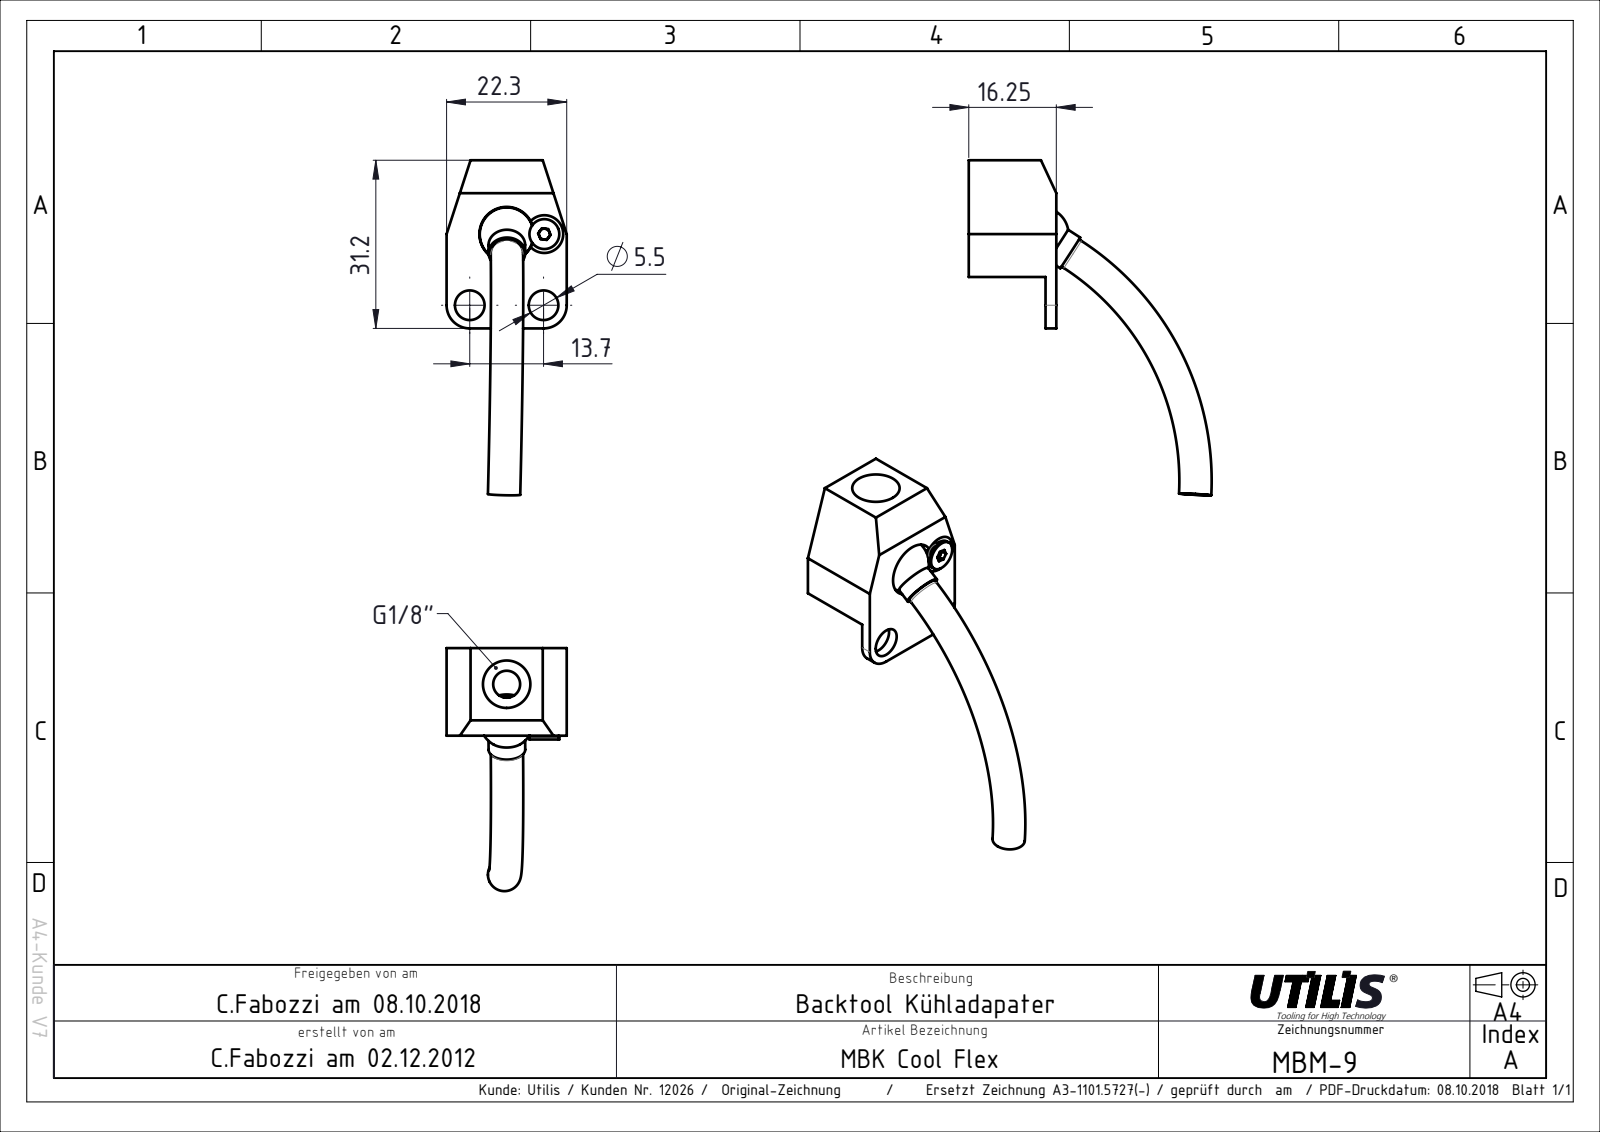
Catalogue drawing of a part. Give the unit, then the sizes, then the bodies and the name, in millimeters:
Units: millimetres
Overall size (bounding box): 62.16 × 45.09 × 22.3
Round holes (diameter × count): ⌀5.5 ×2, ⌀5 ×1
Round bosses / shafts (diameter × count): ⌀6.8 ×1, ⌀6 ×1, ⌀5.54 ×1, ⌀3 ×1
Partial cylindrical surfaces — rounded edges, fillets, slot ends (radius × count): R4.3 ×2, R26.5 ×1
Main face-to-face distances: 16.25, 14.25, 2, 22.3, 31.2, 16.96, 2.71, 0.71, 10, 8.96
Hole centre spacings: 13.7
Volume: 7 420 mm³ · Surface area: 4 964 mm²
Bodies: 3 solids, 58 faces (27 planar, 17 cylindrical, 14 other)
Part name (STEP PRODUCT): MSP-88_UTILIS Multidec Senkschraube; MBM-9_01; MBM-9; Riehetec-1_01
STEP written by: SolidWorks 2018 (CONFIG_CONTROL_DESIGN)
